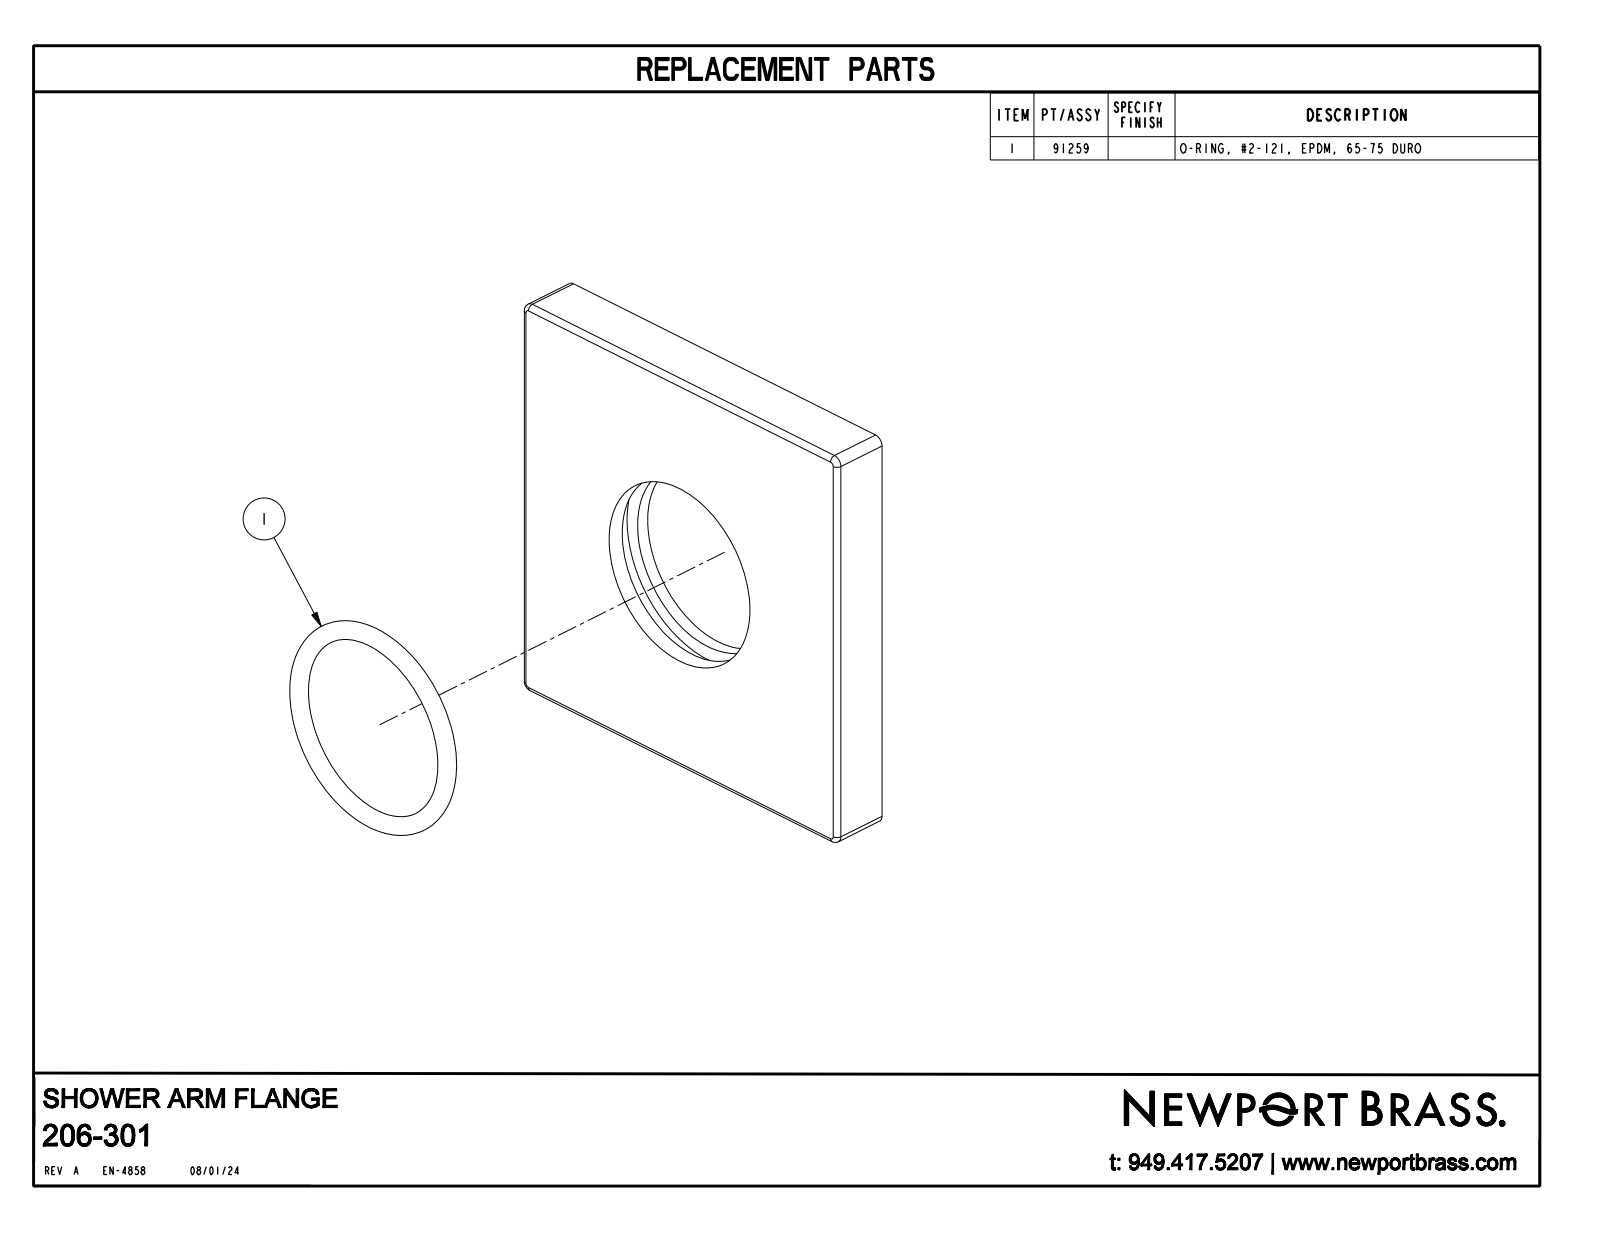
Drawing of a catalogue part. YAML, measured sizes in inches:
part_name: "206-301"
step_written_by: "CREO PARAMETRIC BY PTC INC, 2023134 (CONFIG_CONTROL_DESIGN)"
units: inches
bodies: {solids: 2, faces: 42, planar: 14, cylindrical: 20, other: 8}
overall_size: [2.45, 2.45, 0.35]
volume: 1.014
surface_area: 19
round_holes:
  - {diameter: 1.095, count: 1}
  - {diameter: 1.26, count: 1}
round_bosses_or_shafts:
  - {diameter: 1.455, count: 1}
partial_cylinders:
  - {radius: 0.03, count: 4}
  - {radius: 0.05, count: 4}
  - {radius: 0.125, count: 4}
face_to_face_distances: [0.125, 2.325, 2.45, 0.225, 0.35, 2.2, 0.05, 0.175, 0.3, 0.128]
